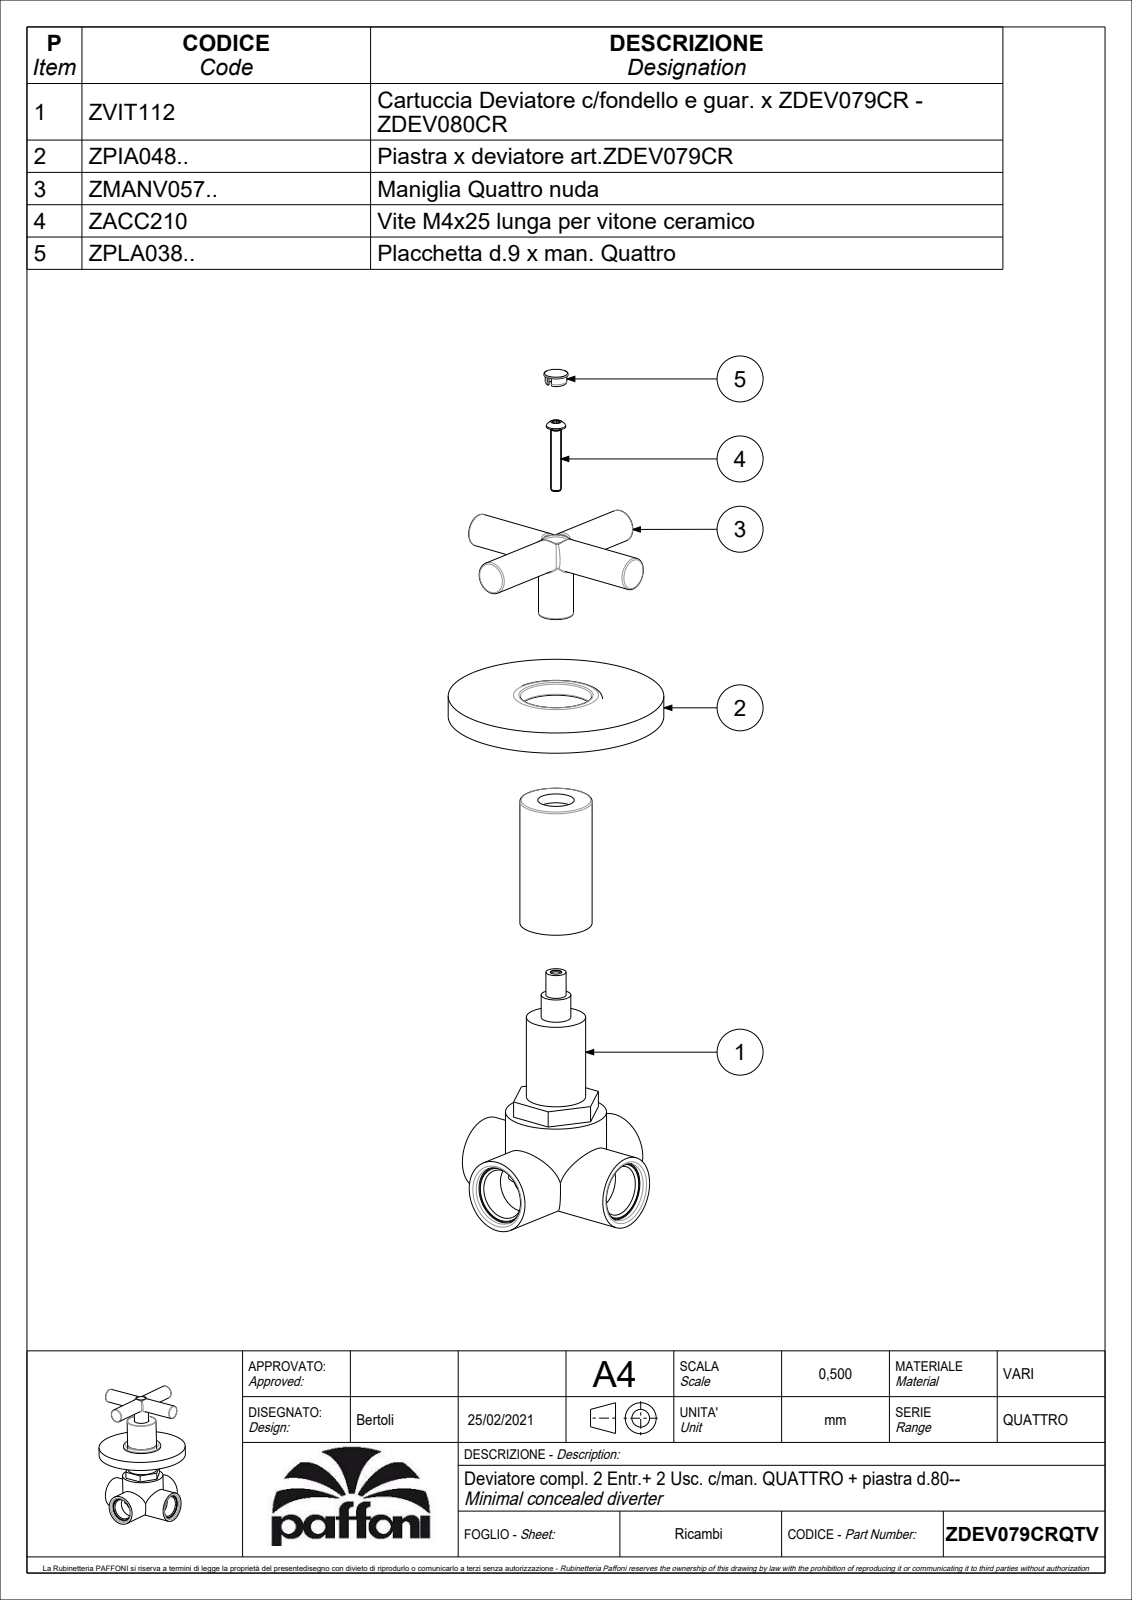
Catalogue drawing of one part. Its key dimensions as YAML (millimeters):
part_name: "ZDEV079CRQTV"
step_written_by: "CREO PARAMETRIC BY PTC INC, 2020044 (CONFIG_CONTROL_DESIGN)"
units: millimeters
bodies: {solids: 1, faces: 216, planar: 88, cylindrical: 52, other: 76}
overall_size: [80, 80, 59.7]
volume: 46145
surface_area: 26520
round_holes:
  - {diameter: 3.3, count: 1}
  - {diameter: 4.5, count: 1}
  - {diameter: 7, count: 1}
  - {diameter: 8, count: 1}
  - {diameter: 13.5, count: 1}
  - {diameter: 20.7, count: 1}
  - {diameter: 24, count: 1}
  - {diameter: 76, count: 1}
round_bosses_or_shafts:
  - {diameter: 12, count: 2}
  - {diameter: 80, count: 1}
  - {diameter: 34.5, count: 1}
  - {diameter: 31, count: 1}
  - {diameter: 27, count: 1}
  - {diameter: 22, count: 1}
  - {diameter: 13, count: 1}
  - {diameter: 11, count: 1}
partial_cylinders:
  - {radius: 3, count: 1}
  - {radius: 4.75, count: 1}
face_to_face_distances: [2, 6, 8, 1, 36.5, 30.5, 28.5, 3.5, 26, 29.5]
